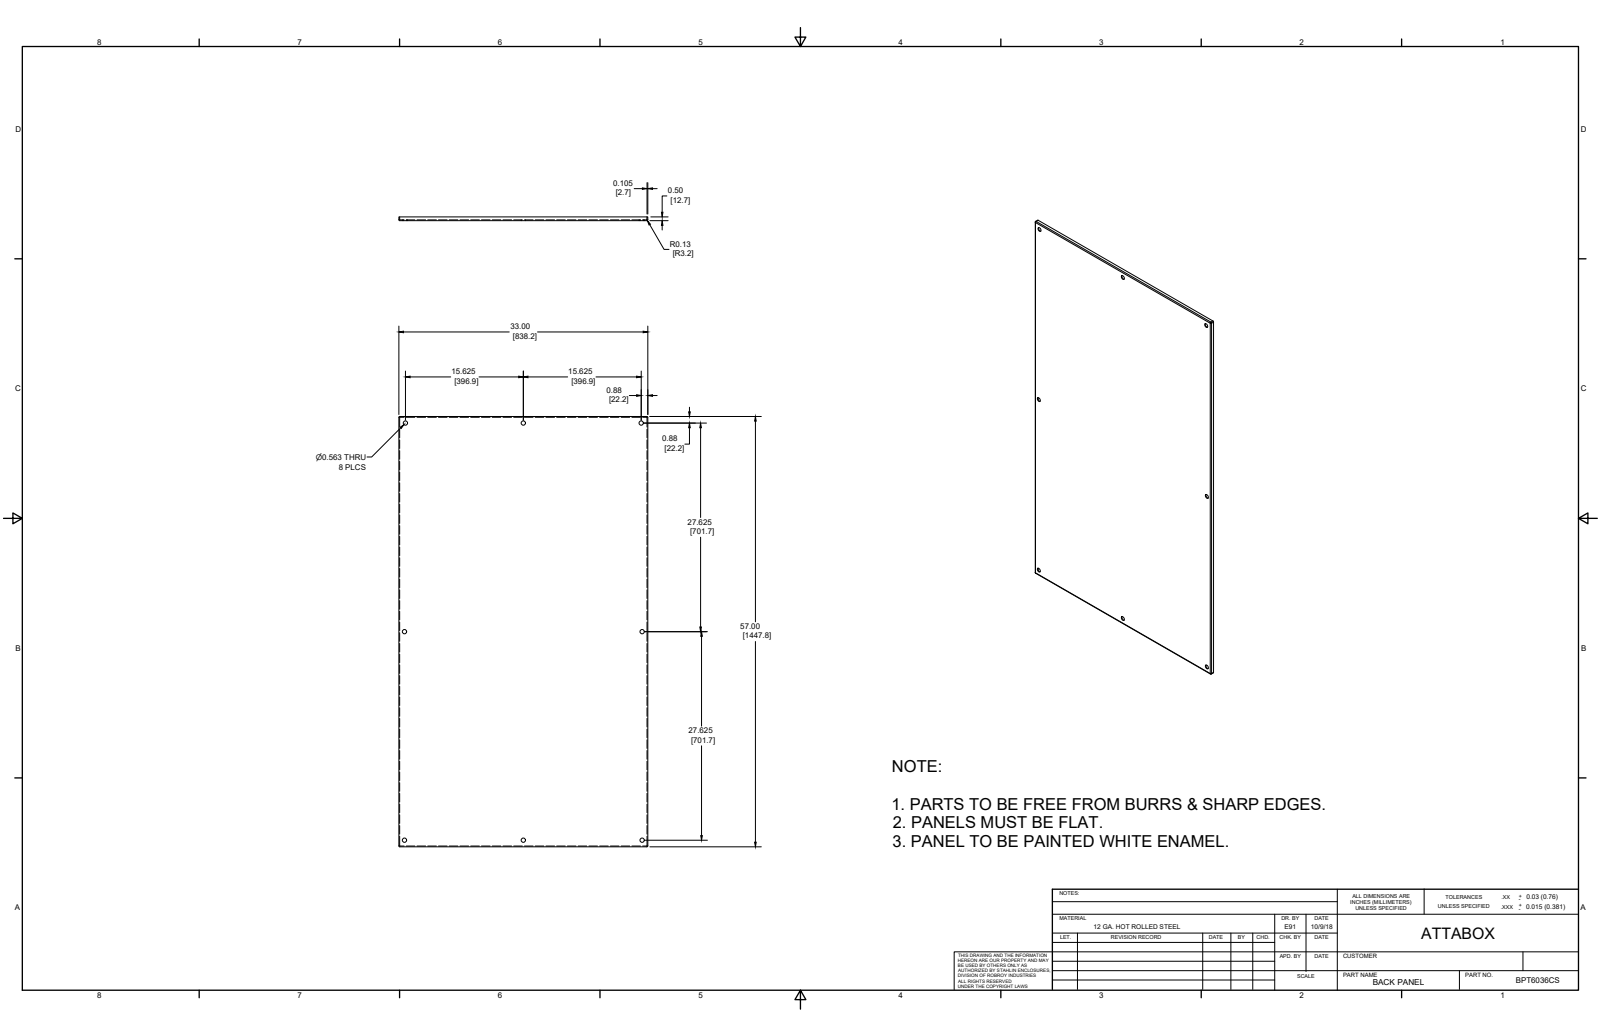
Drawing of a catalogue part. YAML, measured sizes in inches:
part_name: "BP6036CS_STP"
step_written_by: "Autodesk Inventor 2014 (AUTOMOTIVE_DESIGN)"
units: inches
bodies: {solids: 1, faces: 43, planar: 11, cylindrical: 24, other: 8}
overall_size: [57, 33, 0.5]
volume: 204.1
surface_area: 3909
round_holes:
  - {diameter: 0.563, count: 8}
partial_cylinders:
  - {radius: 0.02, count: 8}
  - {radius: 0.125, count: 8}
face_to_face_distances: [0.105, 32.895, 56.895, 33, 32.79, 0.395, 0.5, 57, 56.79]
hole_center_spacings: [31.799, 55.25, 15.625, 15.75, 27.625, 27.625, 31.5, 41.804]
